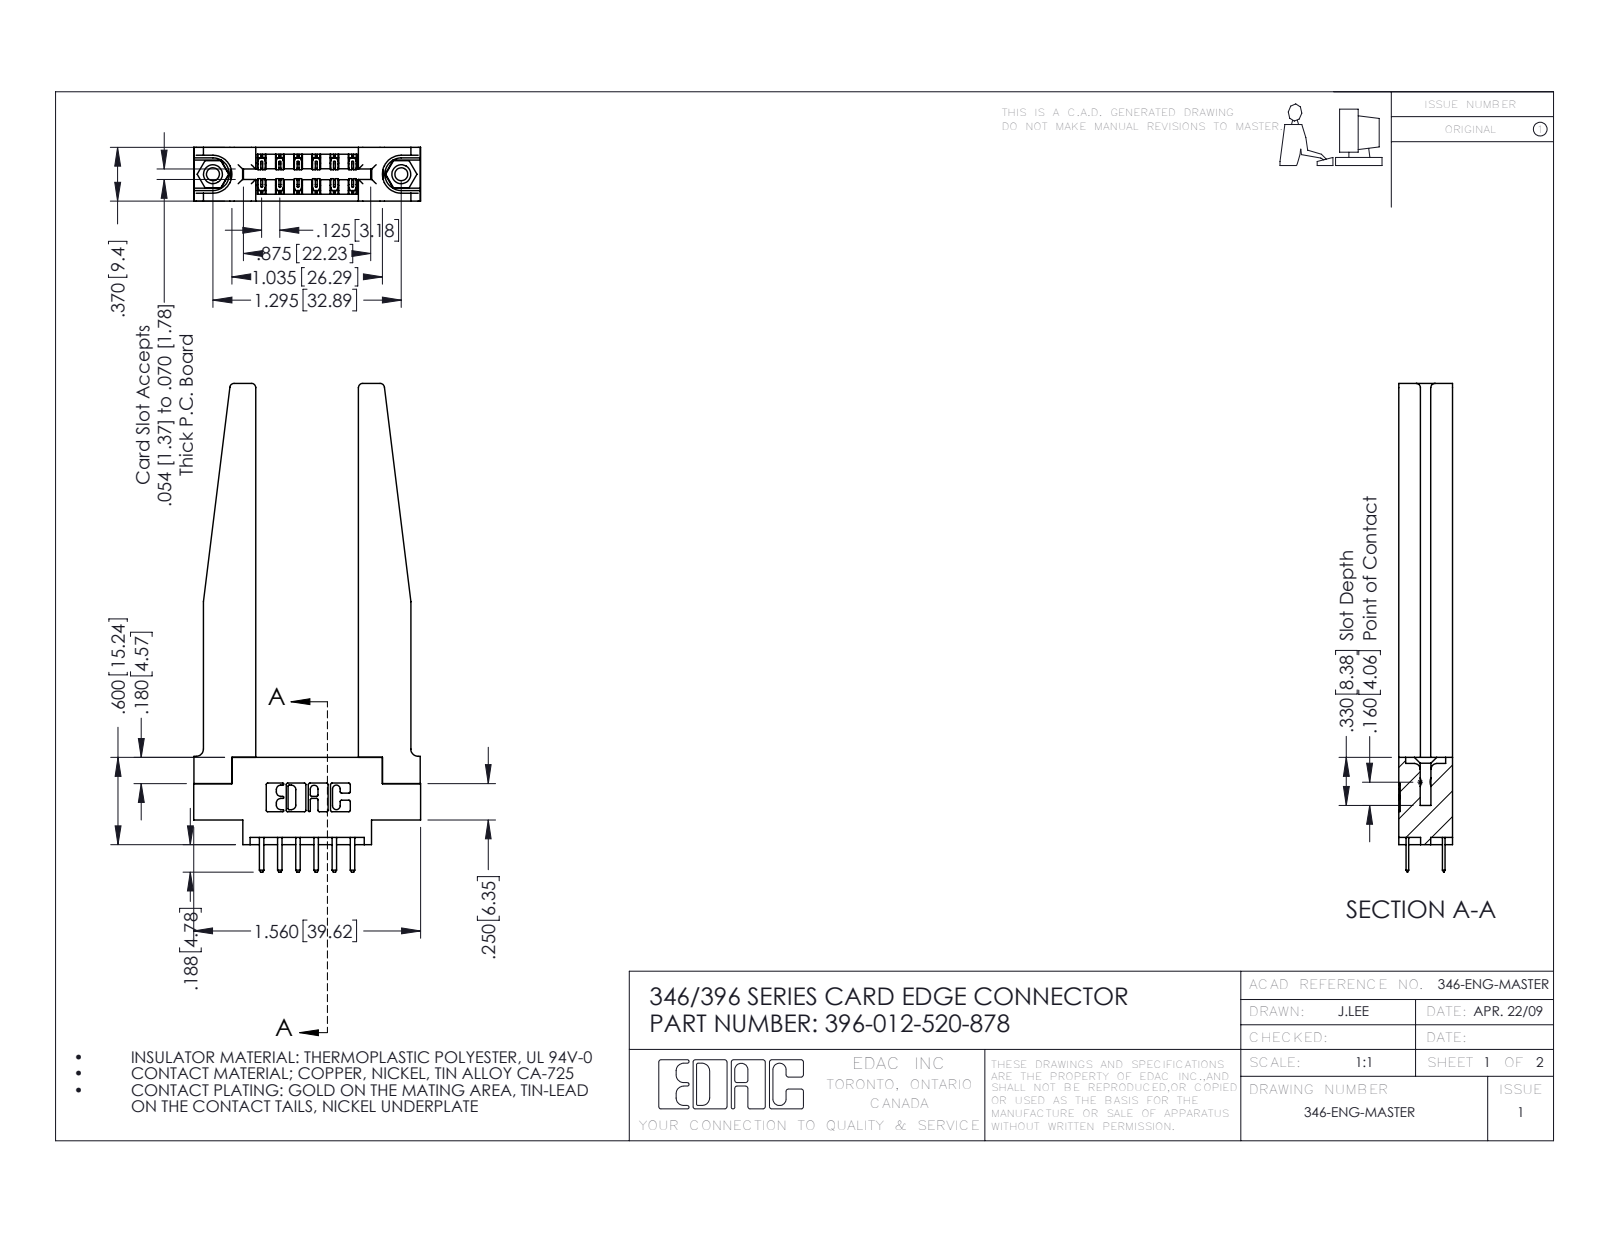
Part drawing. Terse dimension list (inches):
name: 346-220-078_345-220-078; 396-012-520-878; 346 Part_0.170 Offset - 0.156 Dia-TH; 345-250-001_345-250-001-102 (+1 more)
written by: SolidWorks 2016 (CONFIG_CONTROL_DESIGN)
unit: in
bodies: 17 solids, 1032 faces (666 planar, 314 cylindrical, 52 other)
size: 3.358 × 1.56 × 0.37
volume: 0.631 in³; area: 16.81 in²
holes: 2× ⌀0.089, 2× ⌀0.125, 2× ⌀0.156, 1× ⌀0.064
bosses: 2× ⌀0.155
rounds: 22× R0.01, 18× R0.006, 16× R0.01, 8× R0.03, 6× R0.007, 6× R0.031, 3× R0.026, 2× R0.014
face distances: 0.37, 0.15, 0.22, 0.25, 0.706, 0.148, 0.072, 0.102, 0.048, 0.322
hole spacings: 0.246, 1.092, 1.295
